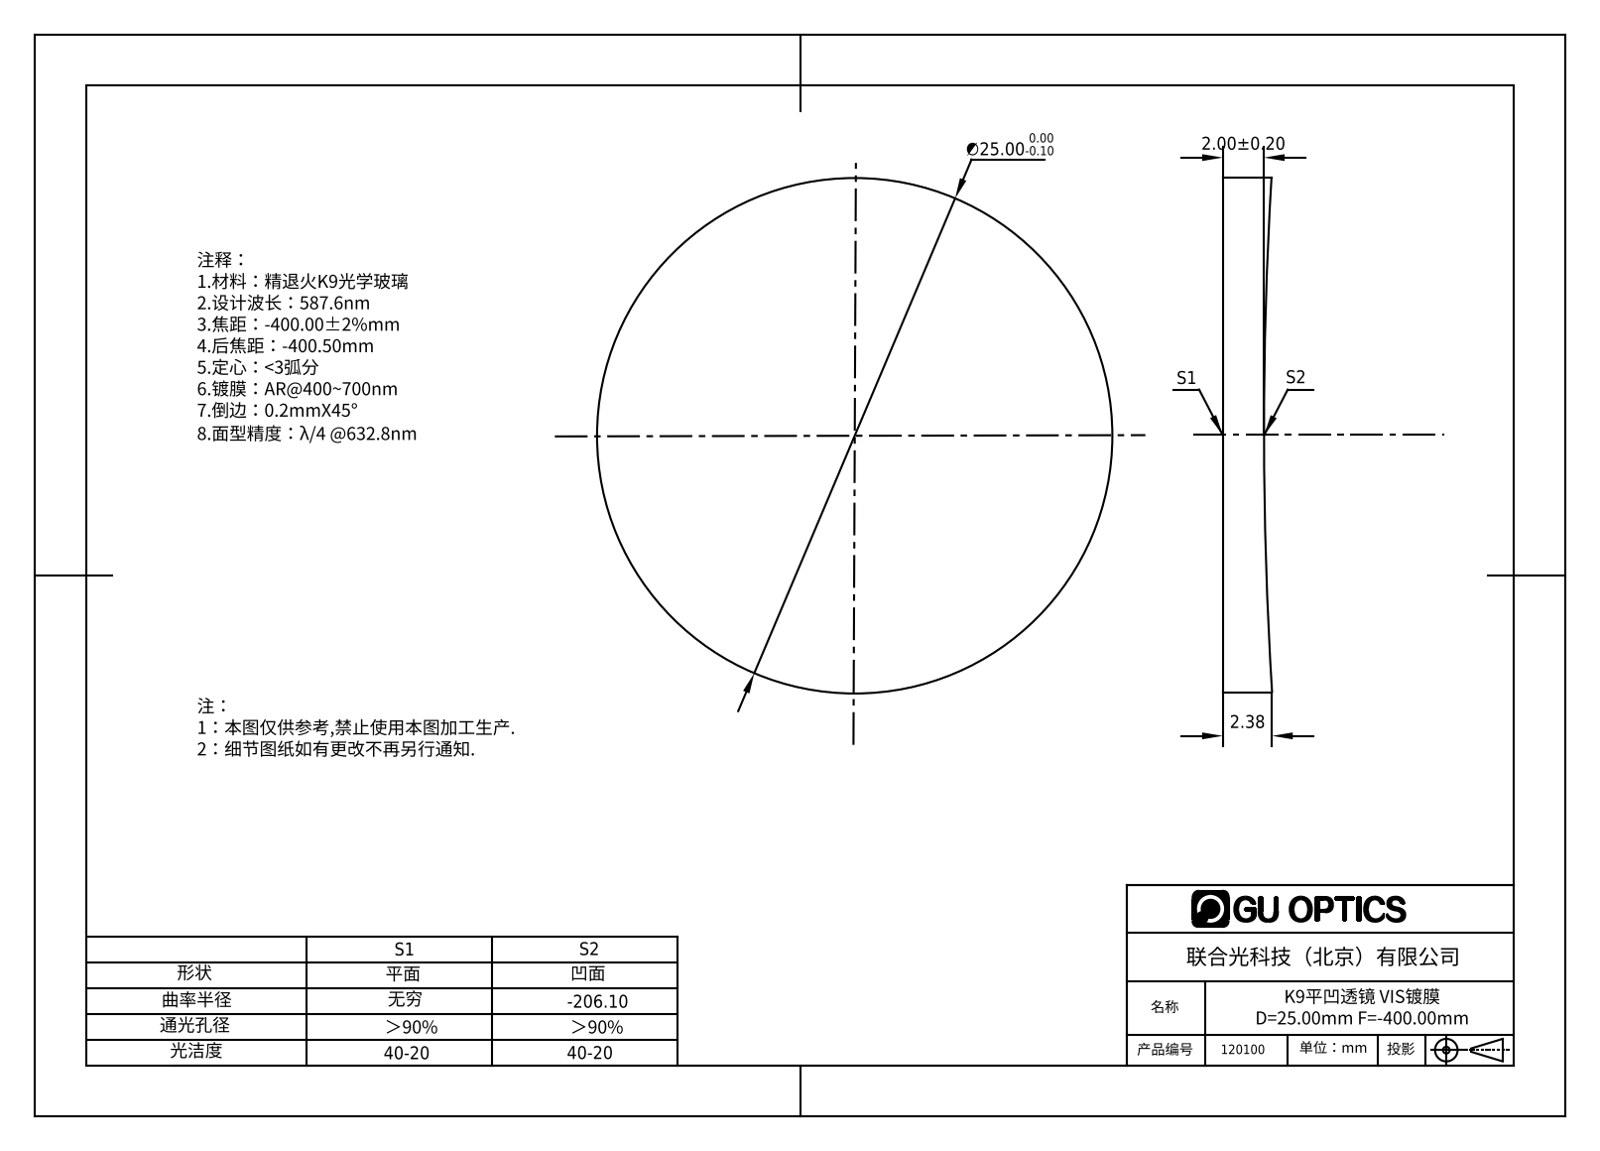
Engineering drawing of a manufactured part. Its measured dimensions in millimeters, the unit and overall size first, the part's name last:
Units: millimetres
Overall size (bounding box): 25 × 25 × 2.37
Round bosses / shafts (diameter × count): ⌀25 ×1
Volume: 1 070 mm³ · Surface area: 1 168 mm²
Bodies: 1 solid, 5 faces (1 planar, 2 cylindrical, 2 other)
Part name (STEP PRODUCT): 120040
STEP written by: SolidWorks 2016 (AUTOMOTIVE_DESIGN)
